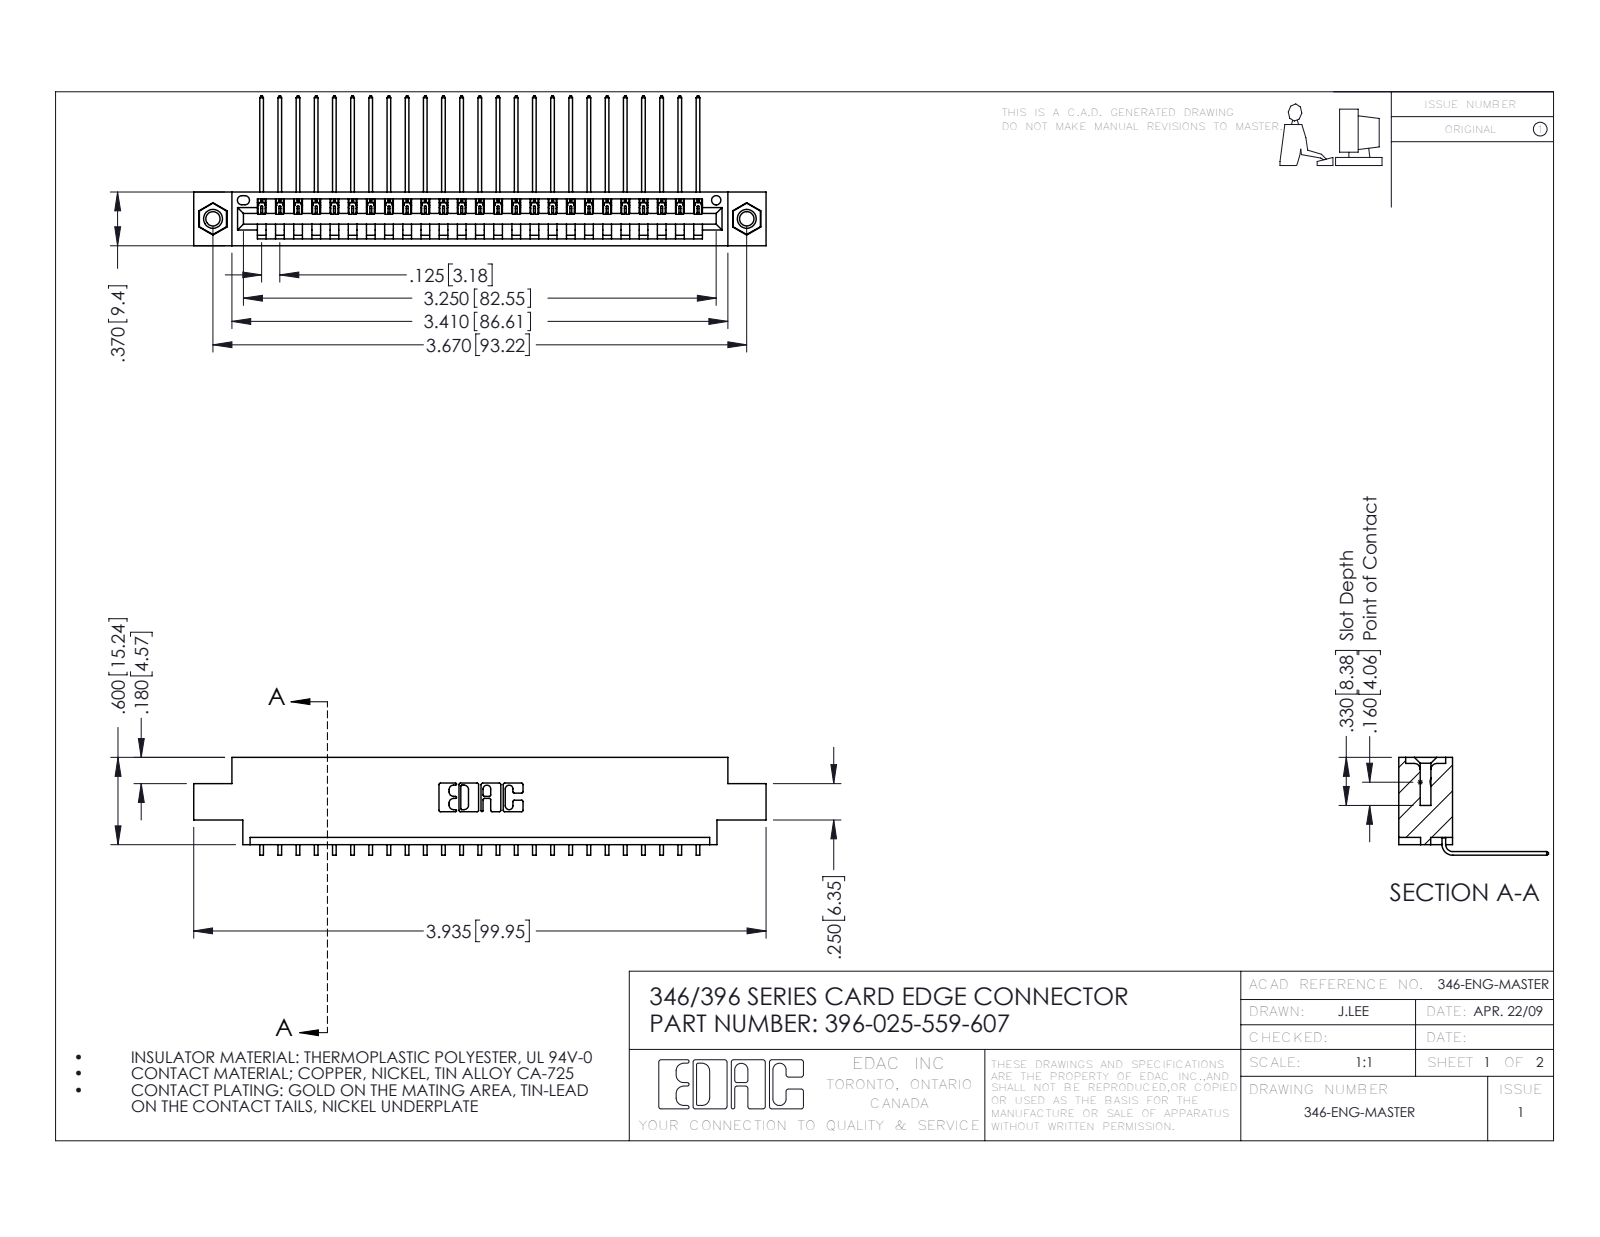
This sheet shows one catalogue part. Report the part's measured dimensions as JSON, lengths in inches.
{"part_name": "346 Part_0.170 Offset - 0.156 Dia-TI; 345-292-001_558 559 Tail - 1; 396-025-559-607; 345-250-001_345-250-005-103", "step_written_by": "SolidWorks 2016 (CONFIG_CONTROL_DESIGN)", "units": "inches", "bodies": {"solids": 28, "faces": 1686, "planar": 1162, "cylindrical": 508, "other": 16}, "overall_size": [3.935, 1.03, 0.673], "volume_in3": 0.572, "surface_area_in2": 18.93, "round_holes": [[0.098, 2], [0.125, 2], [0.156, 2], [0.064, 1]], "round_bosses_or_shafts": [[0.155, 2]], "partial_cylinders_radius": [[0.006, 50], [0.01, 22], [0.007, 6], [0.031, 6], [0.026, 3], [0.031, 2], [0.04, 2], [0.014, 1]], "face_to_face_distances": [0.048, 0.322, 0.37, 0.25, 0.025, 0.072, 0.222, 0.148, 0.1, 0.174], "hole_center_spacings": [0.246, 3.462, 3.67]}
